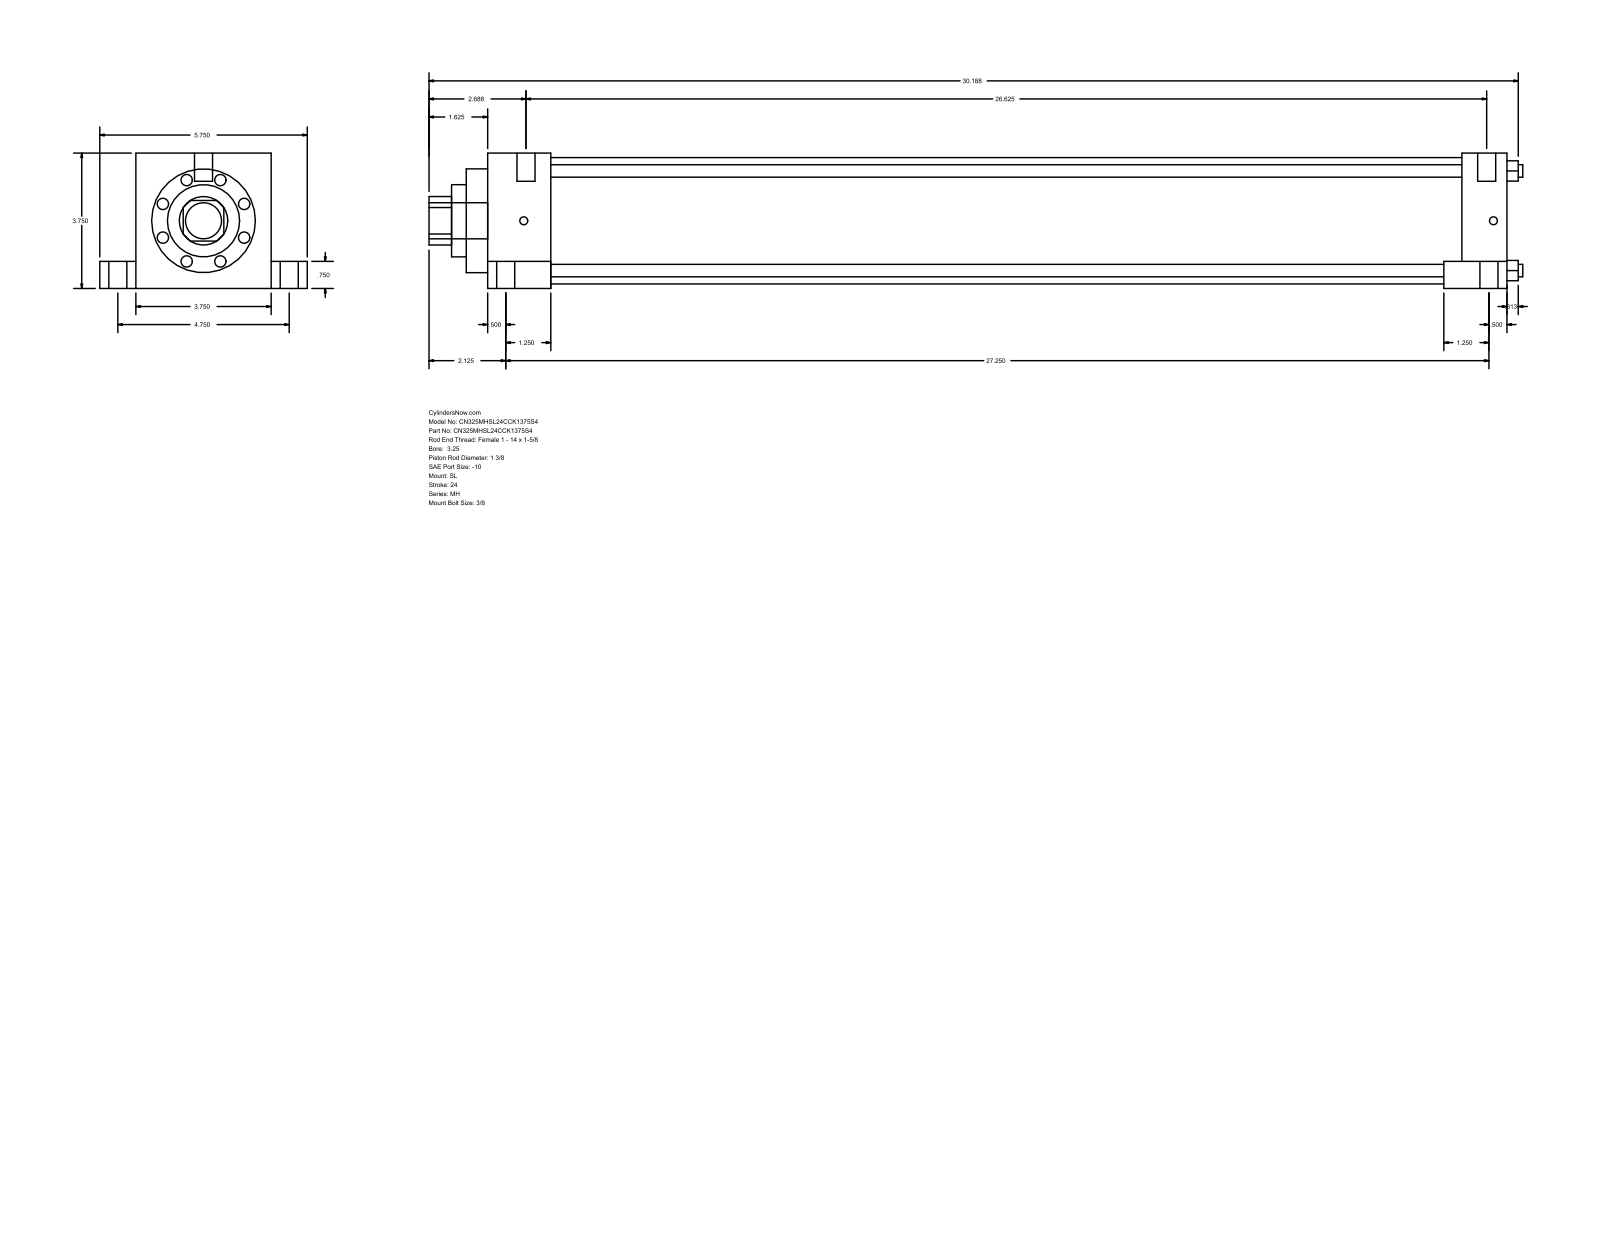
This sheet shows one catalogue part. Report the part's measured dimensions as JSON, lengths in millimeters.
{"part_name": "MH_SL__0325_1.375", "step_written_by": "GSSL Pune (CONFIG_CONTROL_DESIGN)", "units": "millimeters", "bodies": {"solids": 0, "faces": 110, "planar": 77, "cylindrical": 33, "other": 0}, "overall_size": [769.94, 146.05, 95.25], "round_holes": [[8.76, 4], [34.92, 1], [50.8, 1], [73.03, 1], [88.9, 1]], "round_bosses_or_shafts": [[12.7, 6], [19.05, 4], [5.56, 4], [25.4, 1]], "partial_cylinders_radius": [[17.06, 1]], "face_to_face_distances": [95.24, 717.56, 44.45, 673.11, 25.41, 120.65, 19.05, 76.19, 685.81, 641.36], "hole_center_spacings": [49.57, 70.1, 99.14]}
